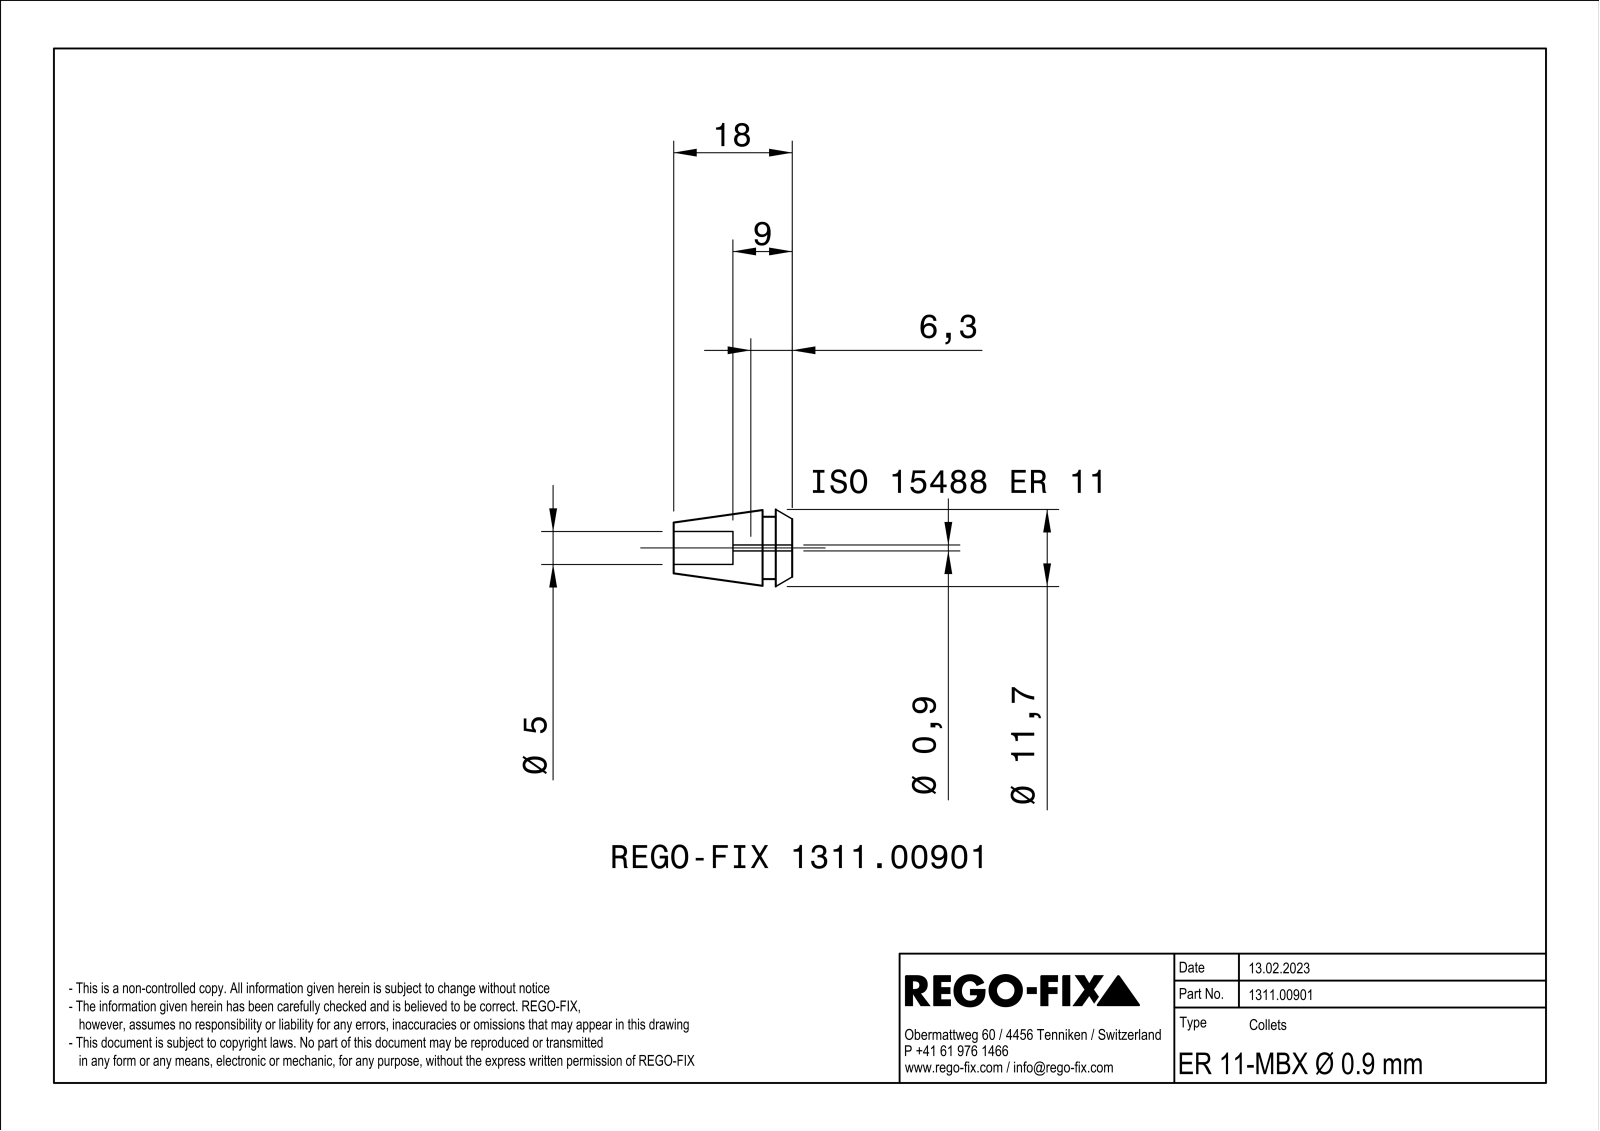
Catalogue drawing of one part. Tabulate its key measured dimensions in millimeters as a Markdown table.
| quantity | value |
| --- | --- |
| part name | NOCUT |
| STEP written by | SIEMENS PLM Software Solid Edge ST10 (AUTOMOTIVE_DESIGN) |
| units | millimeters |
| bodies | 1 solid, 91 faces (26 planar, 19 cylindrical, 46 other) |
| overall size | 18 × 11.41 × 11.39 |
| volume | 988 mm³ |
| surface area | 1 253 mm² |
| round holes (diameter × count) | 1.5 × 3, 5 × 1 |
| round bosses / shafts (diameter × count) | 9.5 × 1 |
| partial cylindrical surfaces (radius × count) | 25 × 3, 0.45 × 1 |
| main face-to-face distances | 0.8, 4.5, 0.54, 18, 13.5, 9, 2.5, 2, 15.5, 6.5 |
| hole center spacings | 1.7, 2.94 |
